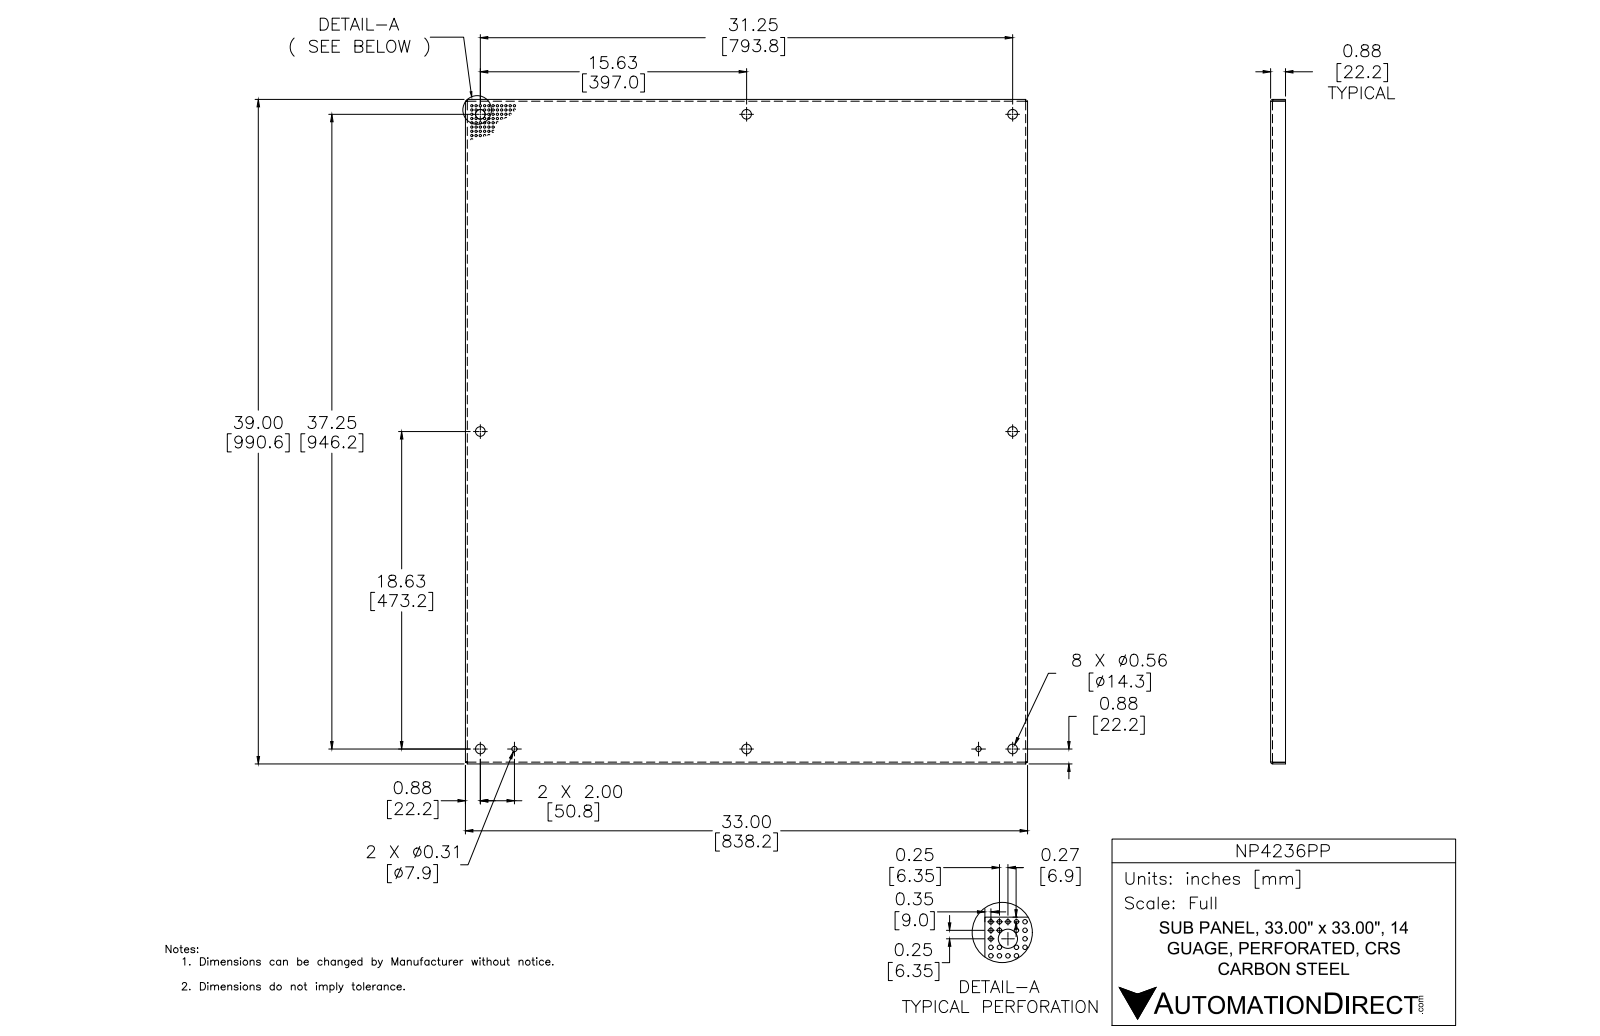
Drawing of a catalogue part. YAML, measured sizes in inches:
part_name: "NP_PP"
step_written_by: "Autodesk Inventor 2014 (AUTOMOTIVE_DESIGN)"
units: inches
bodies: {solids: 1, faces: 48, planar: 22, cylindrical: 18, other: 8}
overall_size: [39, 33, 0.875]
volume: 103.3
surface_area: 2802
round_holes:
  - {diameter: 0.563, count: 8}
  - {diameter: 0.312, count: 2}
partial_cylinders:
  - {radius: 0.031, count: 4}
  - {radius: 0.105, count: 4}
face_to_face_distances: [0.074, 32.926, 38.926, 33, 32.852, 38.852, 39, 0.801, 0.875, 0.126]
hole_center_spacings: [18.625, 36.38, 24.311, 31.25, 13.625, 15.625, 15.625, 18.732]
